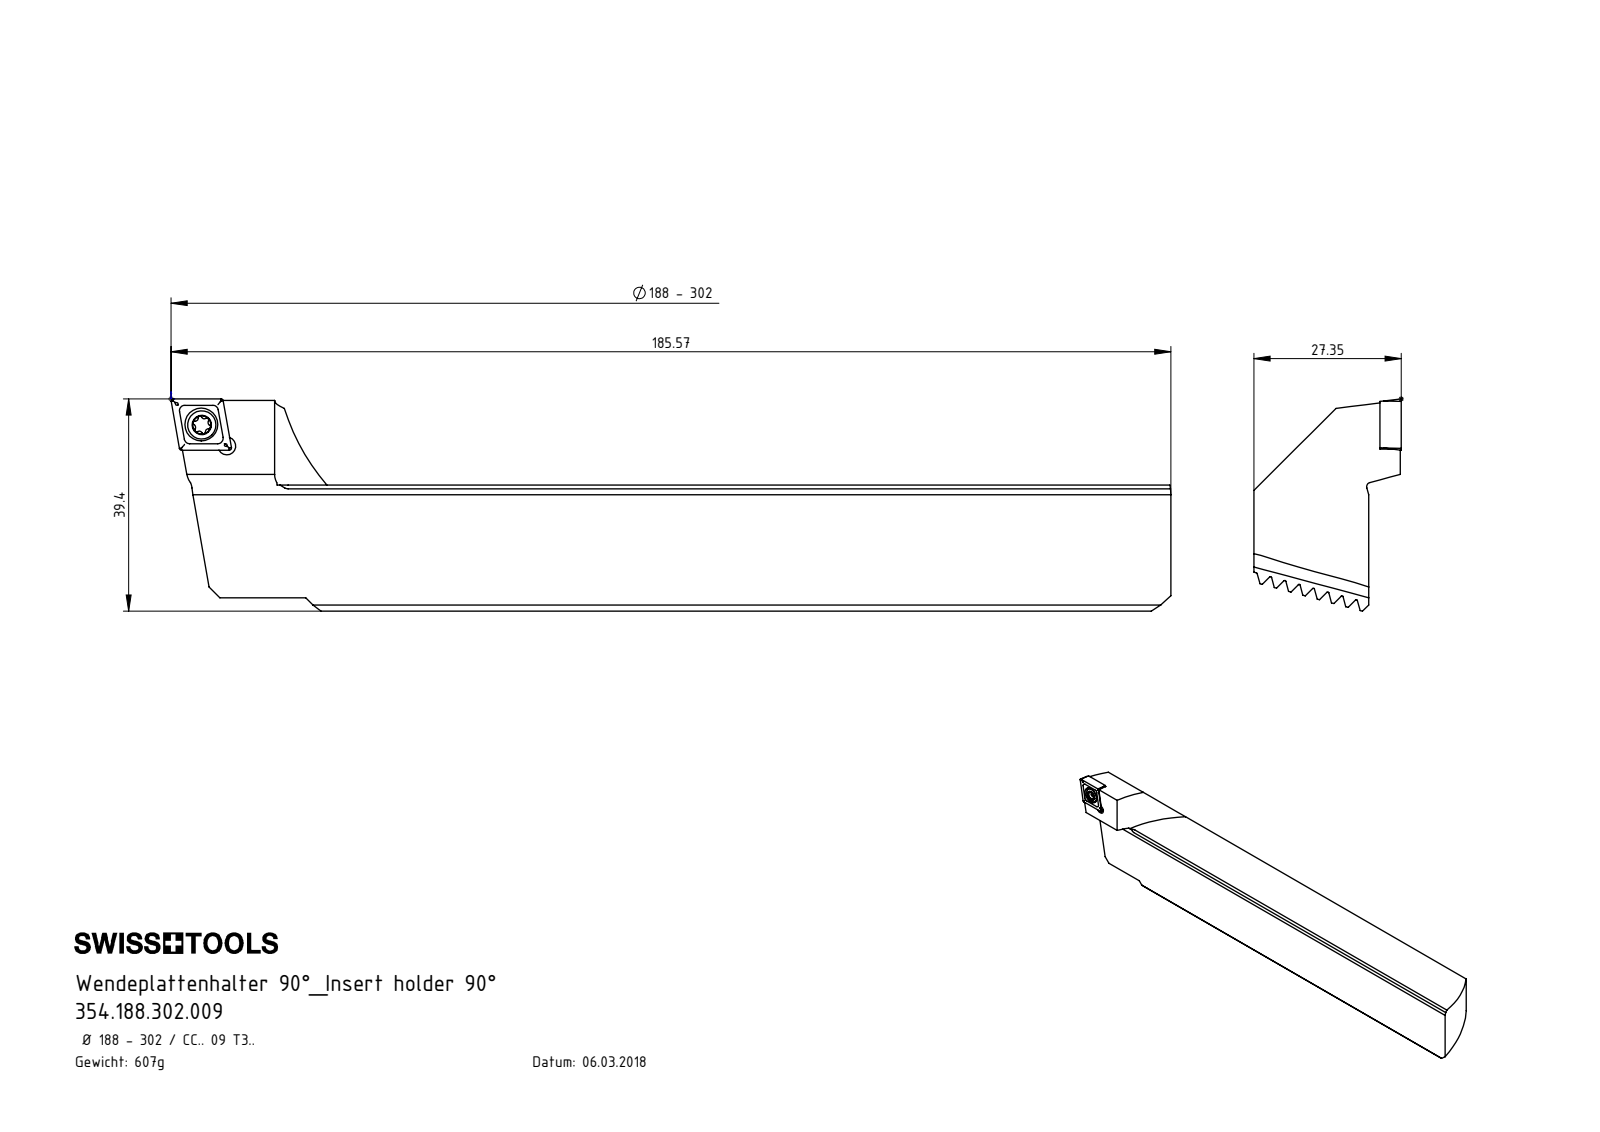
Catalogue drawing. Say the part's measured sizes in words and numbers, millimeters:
The part is named "F00-WCB.188.001_C; WCB-ER2.001.009_A; CCMT09T304; 354.188.302.009". Its 3-D file was written by "SolidWorks 2017 (CONFIG_CONTROL_DESIGN)". It is 3 solids with 694 faces: 422 planar, 39 cylindrical and 233 other. Overall it measures 185.57 by 39.4 by 27.35 millimeters. Its volume is 77 331 cubic millimeters and its surface area 18 926 square millimeters. Round holes: 2 of diameter 3.3, 1 of diameter 4.4, 1 of diameter 6.1. Round bosses or shafts: 1 of diameter 5.25, 1 of diameter 4. Partial cylindrical surfaces (rounded edges, fillets, slot ends): 8 of radius 0.2, 6 of radius 0.34, 6 of radius 0.59, 3 of radius 40, 1 of radius 0.8. The main face-to-face distances are 2.38, 21.3, 4.76, 7.14, 9.52, 4.77, 7.15, 9.53, 11.91, 14.29. The hole center spacings are 6.06, 6.19.
